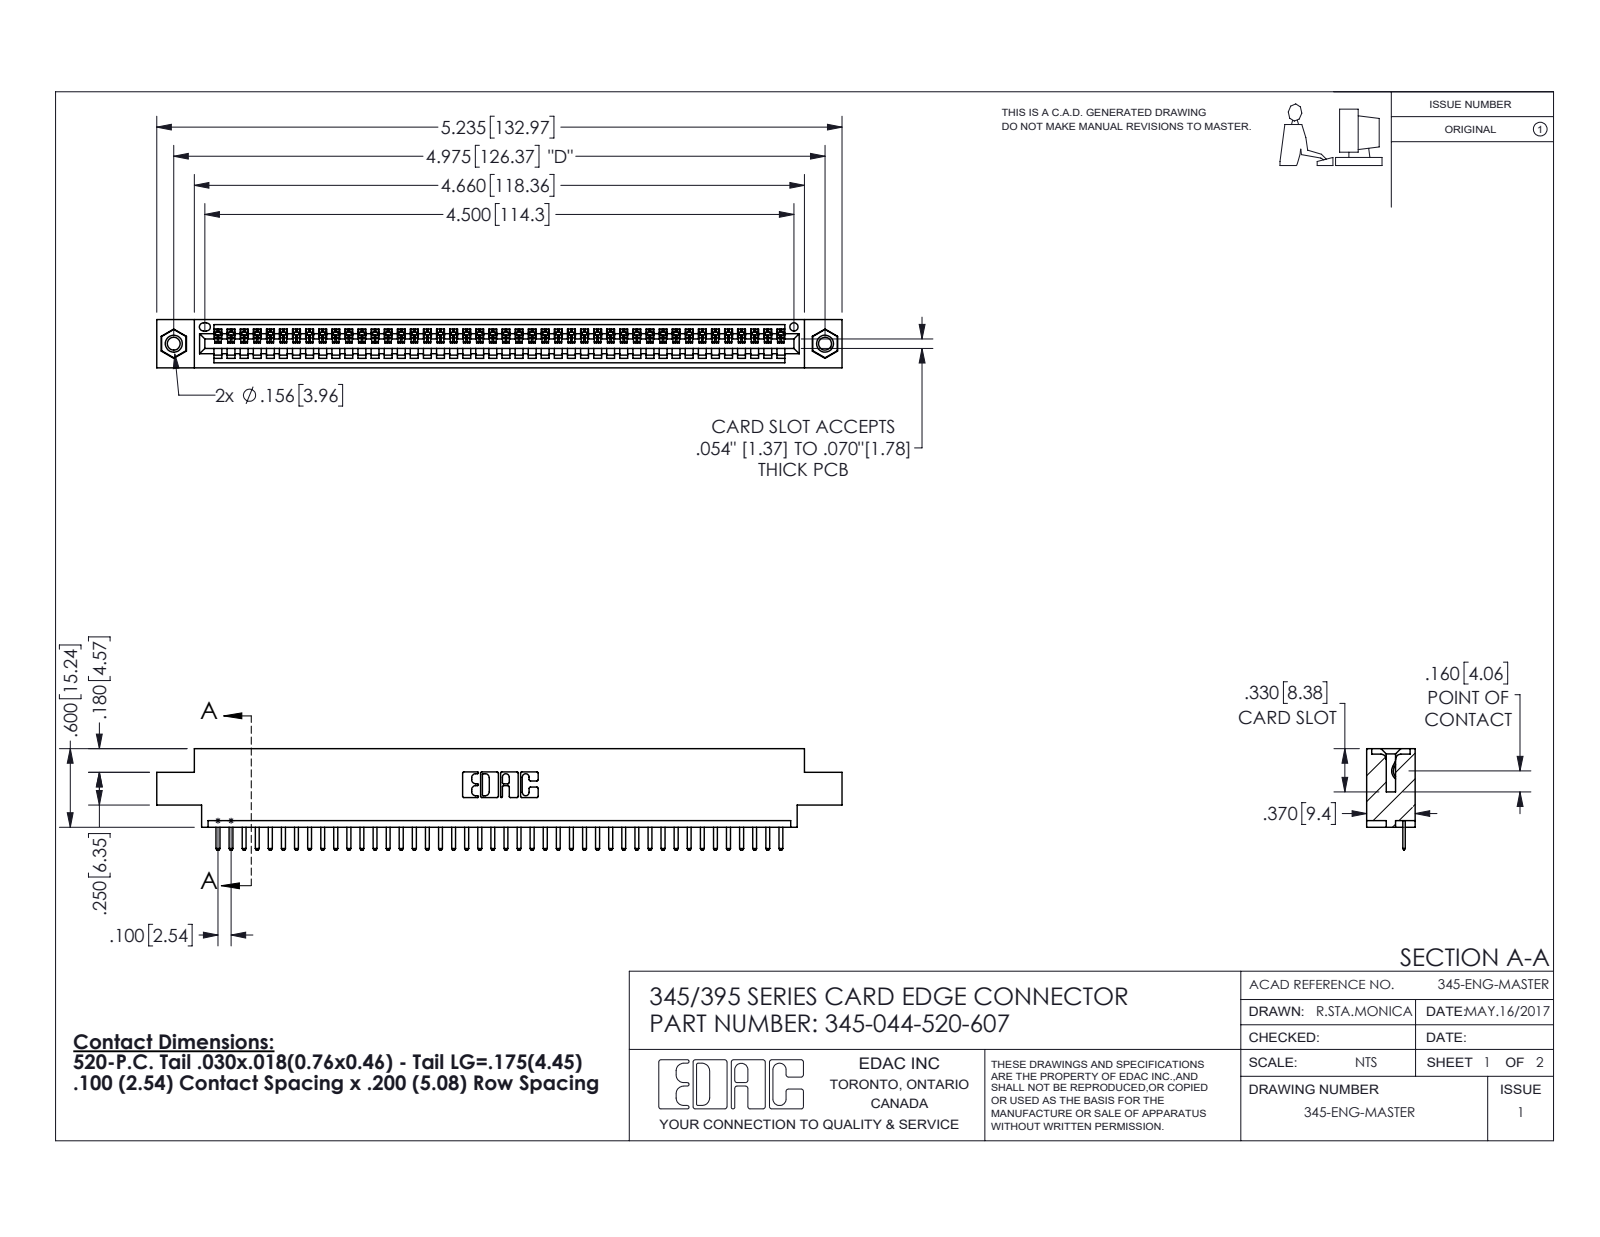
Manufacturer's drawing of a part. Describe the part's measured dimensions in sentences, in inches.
The part is named "345-044-520-607; 345 Part_0.170 Offset - 0.156 Dia-TI; 345-292-001_345-293-120; 345-250-001_345-250-005-103". Its 3-D file was written by "SolidWorks 2016 (CONFIG_CONTROL_DESIGN)". It is 47 solids with 2918 faces: 1964 planar, 938 cylindrical and 16 other. Overall it measures 5.235 by 0.775 by 0.37 inches. Its volume is 0.756 cubic inches and its surface area 25.17 square inches. Round holes: 2 of diameter 0.098, 2 of diameter 0.125, 2 of diameter 0.156, 1 of diameter 0.064. Round bosses or shafts: 2 of diameter 0.155. Partial cylindrical surfaces (rounded edges, fillets, slot ends): 90 of radius 0.01, 88 of radius 0.006, 22 of radius 0.01, 6 of radius 0.007, 6 of radius 0.031, 3 of radius 0.026, 2 of radius 0.031, 2 of radius 0.04. The main face-to-face distances are 0.072, 0.298, 0.37, 0.2, 0.098, 0.272, 0.025, 0.225, 0.072, 0.175. The hole center spacings are 0.27, 4.739, 4.975.
